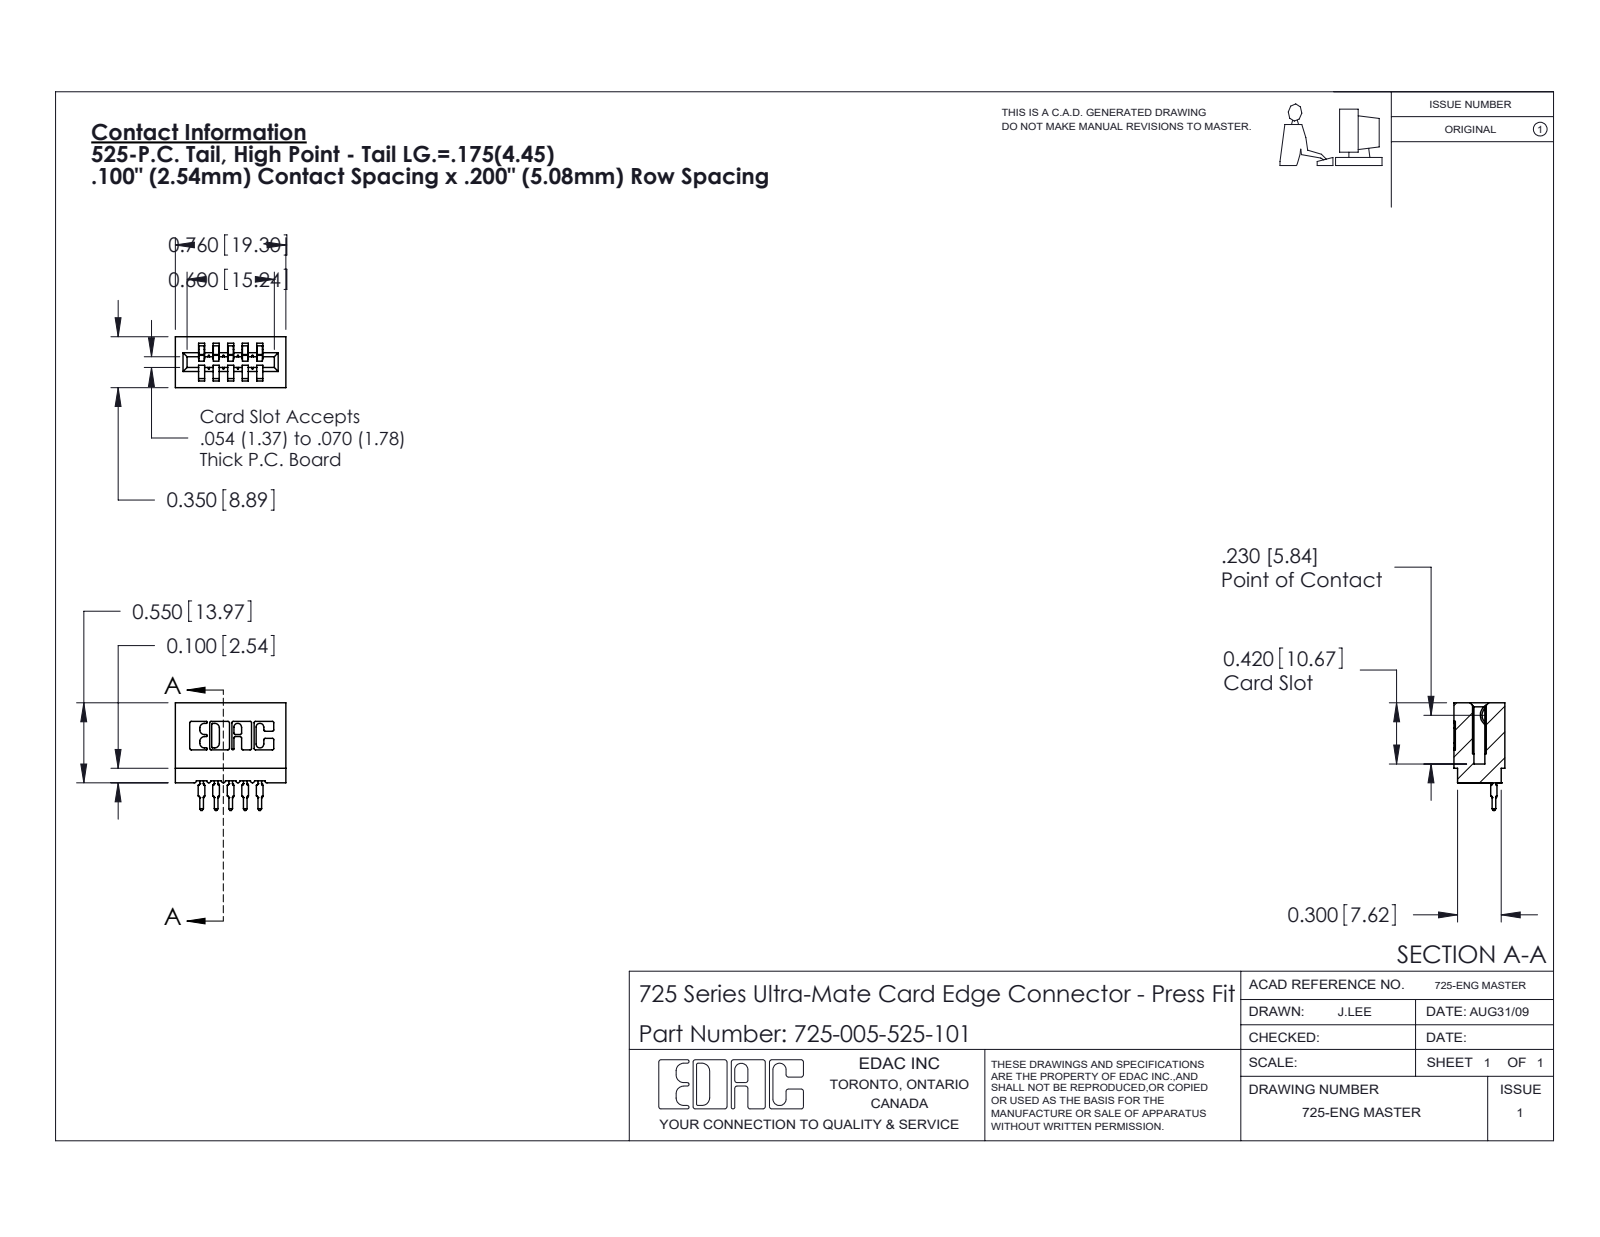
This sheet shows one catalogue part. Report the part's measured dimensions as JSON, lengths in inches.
{"part_name": "745-292-001_525; 725-005-525-101; 725 Part_Insulator Option - 01", "step_written_by": "SolidWorks 2020 (CONFIG_CONTROL_DESIGN)", "units": "inches", "bodies": {"solids": 6, "faces": 655, "planar": 390, "cylindrical": 135, "other": 130}, "overall_size": [0.76, 0.741, 0.35], "volume_in3": 0.102, "surface_area_in2": 3.92, "partial_cylinders_radius": [[0.01, 22], [0.015, 10], [0.021, 10], [0.007, 6], [0.031, 6], [0.005, 4], [0.011, 4], [0.026, 3]], "face_to_face_distances": [0.1, 0.2, 0.042, 0.058, 0.142, 0.3, 0.158, 0.242, 0.212, 0.35]}
